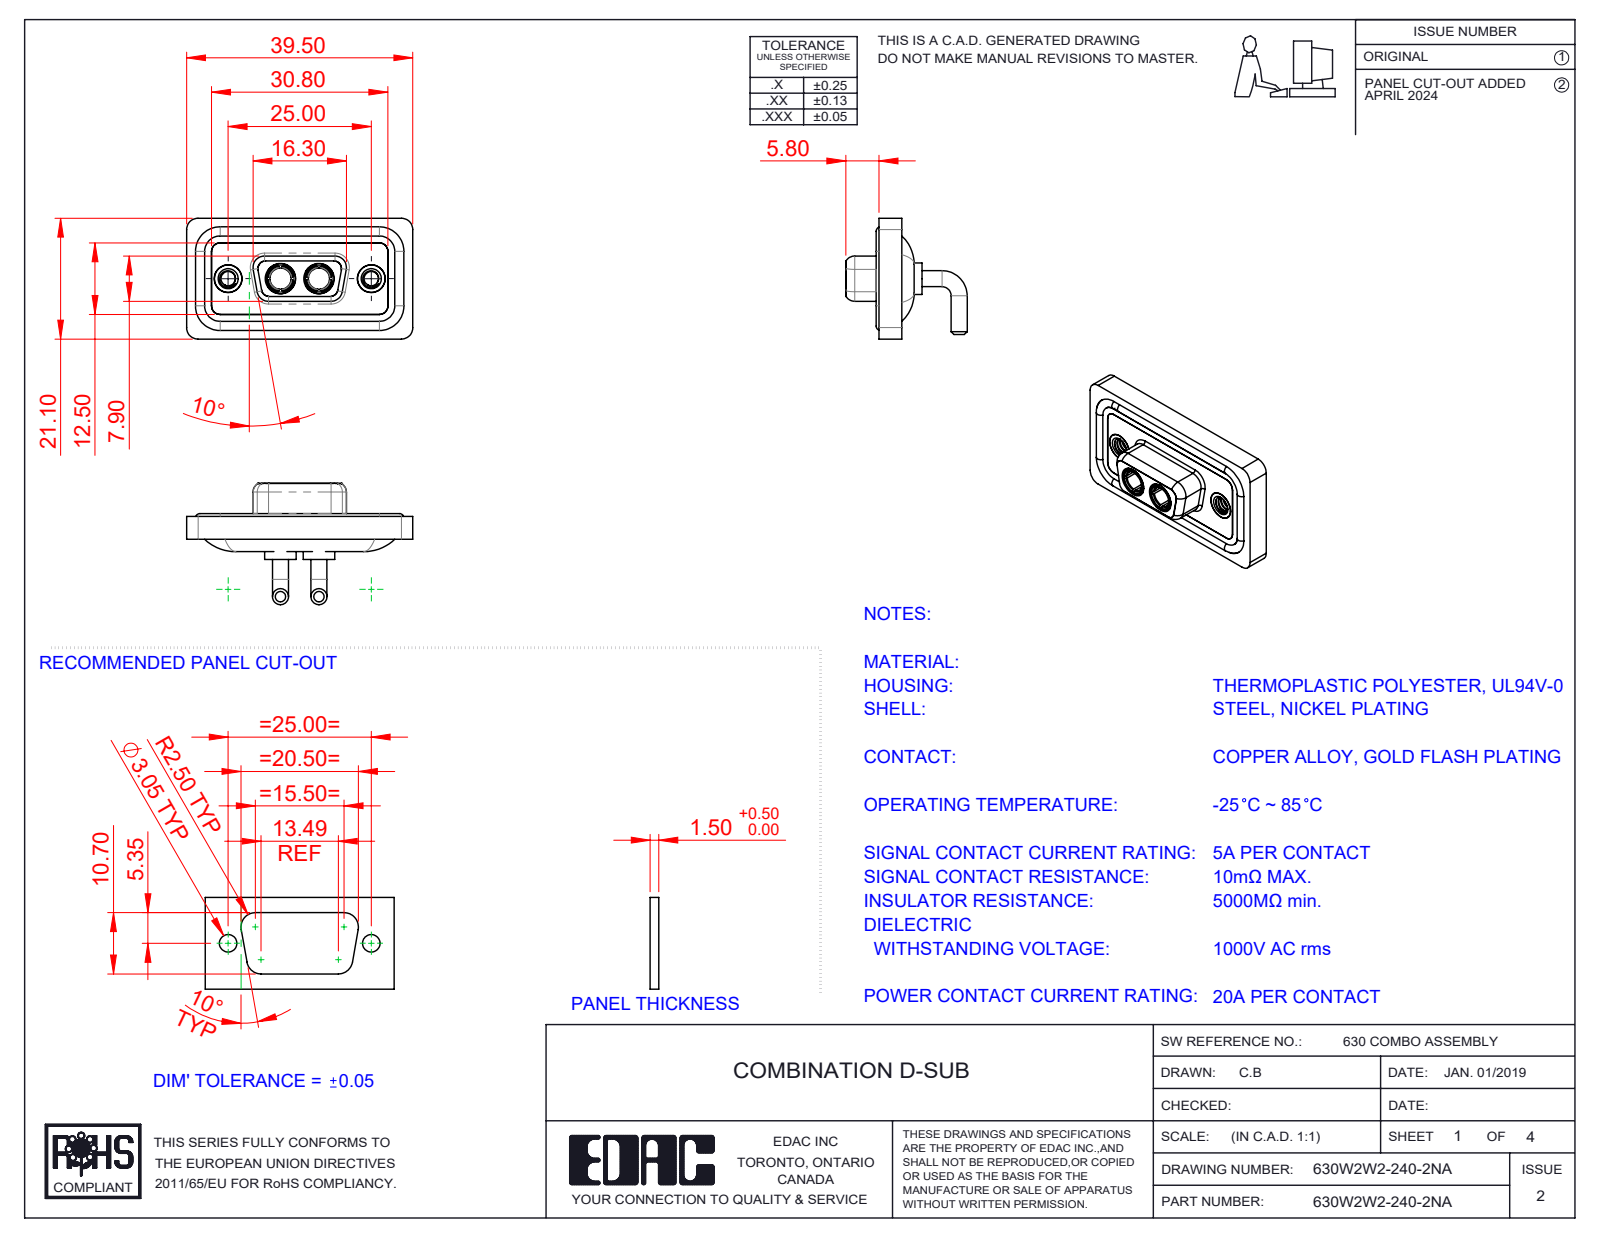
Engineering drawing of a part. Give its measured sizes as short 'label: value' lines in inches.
name: Power Socket_20A RA; 630Combo Shell Rear_09 Contacts; 630W2W2-240-2NA; 630Combo Threaded Rivet_A (+3 more)
written by: SolidWorks 2023 (CONFIG_CONTROL_DESIGN)
unit: in
bodies: 11 solids, 536 faces (163 planar, 236 cylindrical, 137 other)
size: 1.555 × 0.835 × 0.831
volume: 0.293 in³; area: 12.07 in²
holes: 4× ⌀0.191, 2× ⌀0.098, 2× ⌀0.146, 2× ⌀0.157, 2× ⌀0.159, 2× ⌀0.197, 2× ⌀0.209
bosses: 4× ⌀0.11, 4× ⌀0.063, 2× ⌀0.217, 2× ⌀0.205, 2× ⌀0.195, 2× ⌀0.195, 2× ⌀0.189, 2× ⌀0.187
rounds: 18× R0.059, 18× R0.079, 8× R0.053, 8× R0.063, 4× R0.01, 4× R0.02, 4× R0.024, 4× R0.026
face distances: 0.016, 0.071, 0.043, 0.114, 0.098, 0.063, 0.122, 0.059, 0.083, 0.146
hole spacings: 0.36, 0.624, 0.265, 0.984
